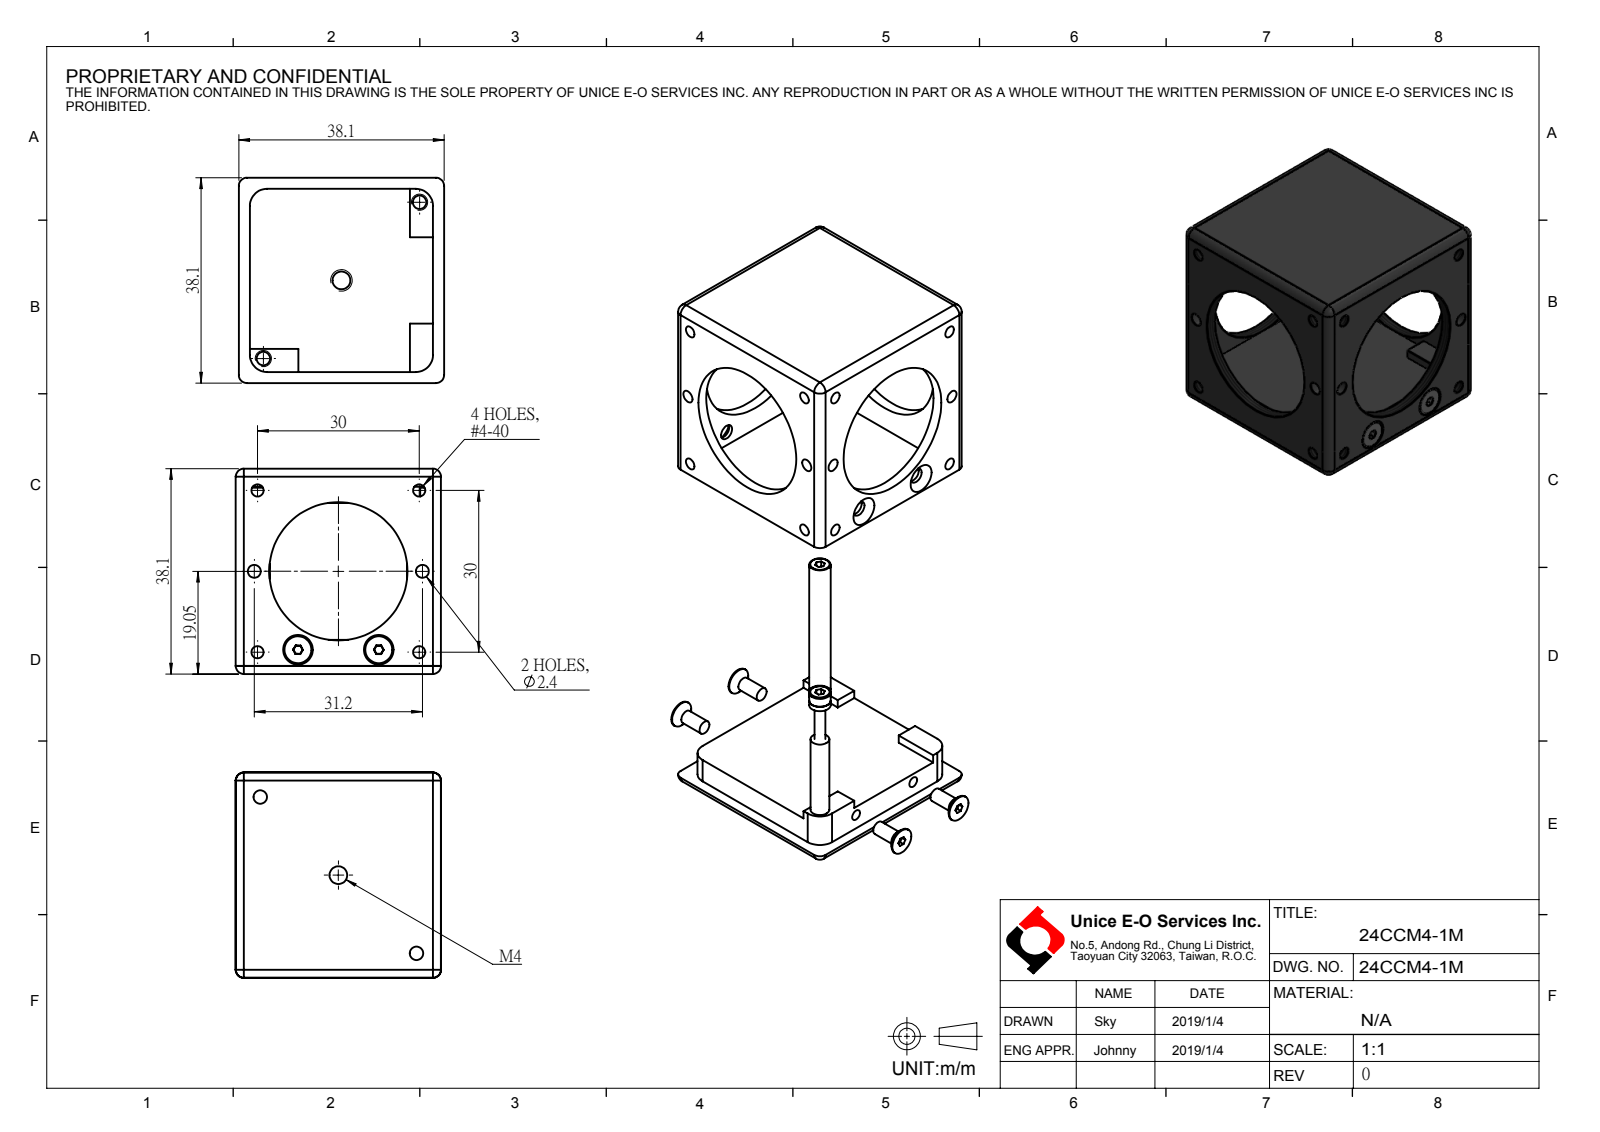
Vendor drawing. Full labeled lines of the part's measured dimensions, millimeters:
Part name (STEP PRODUCT): 24CCM4-1M
STEP written by: SolidWorks 2016 (AUTOMOTIVE_DESIGN)
Units: millimetres
Bodies: 0 solids, 168 faces (62 planar, 90 cylindrical, 16 other)
Overall size (bounding box): 38.1 × 38.1 × 38.1
Round holes (diameter × count): ⌀2.26 ×8, ⌀2.4 ×4, ⌀2.5 ×2, ⌀25.65 ×2, ⌀3.3 ×1
Round bosses / shafts (diameter × count): ⌀5 ×2, ⌀3.5 ×2, ⌀2 ×2
Partial cylindrical surfaces — rounded edges, fillets, slot ends (radius × count): R1.5 ×12
Main face-to-face distances: 38.1, 2.05, 36.05, 6.35, 31.75, 34, 36.6, 1.5, 30.25, 25.4
Hole centre spacings: 15.01, 21.21, 30, 34.08, 15.6, 42.43, 20.51, 31.2
